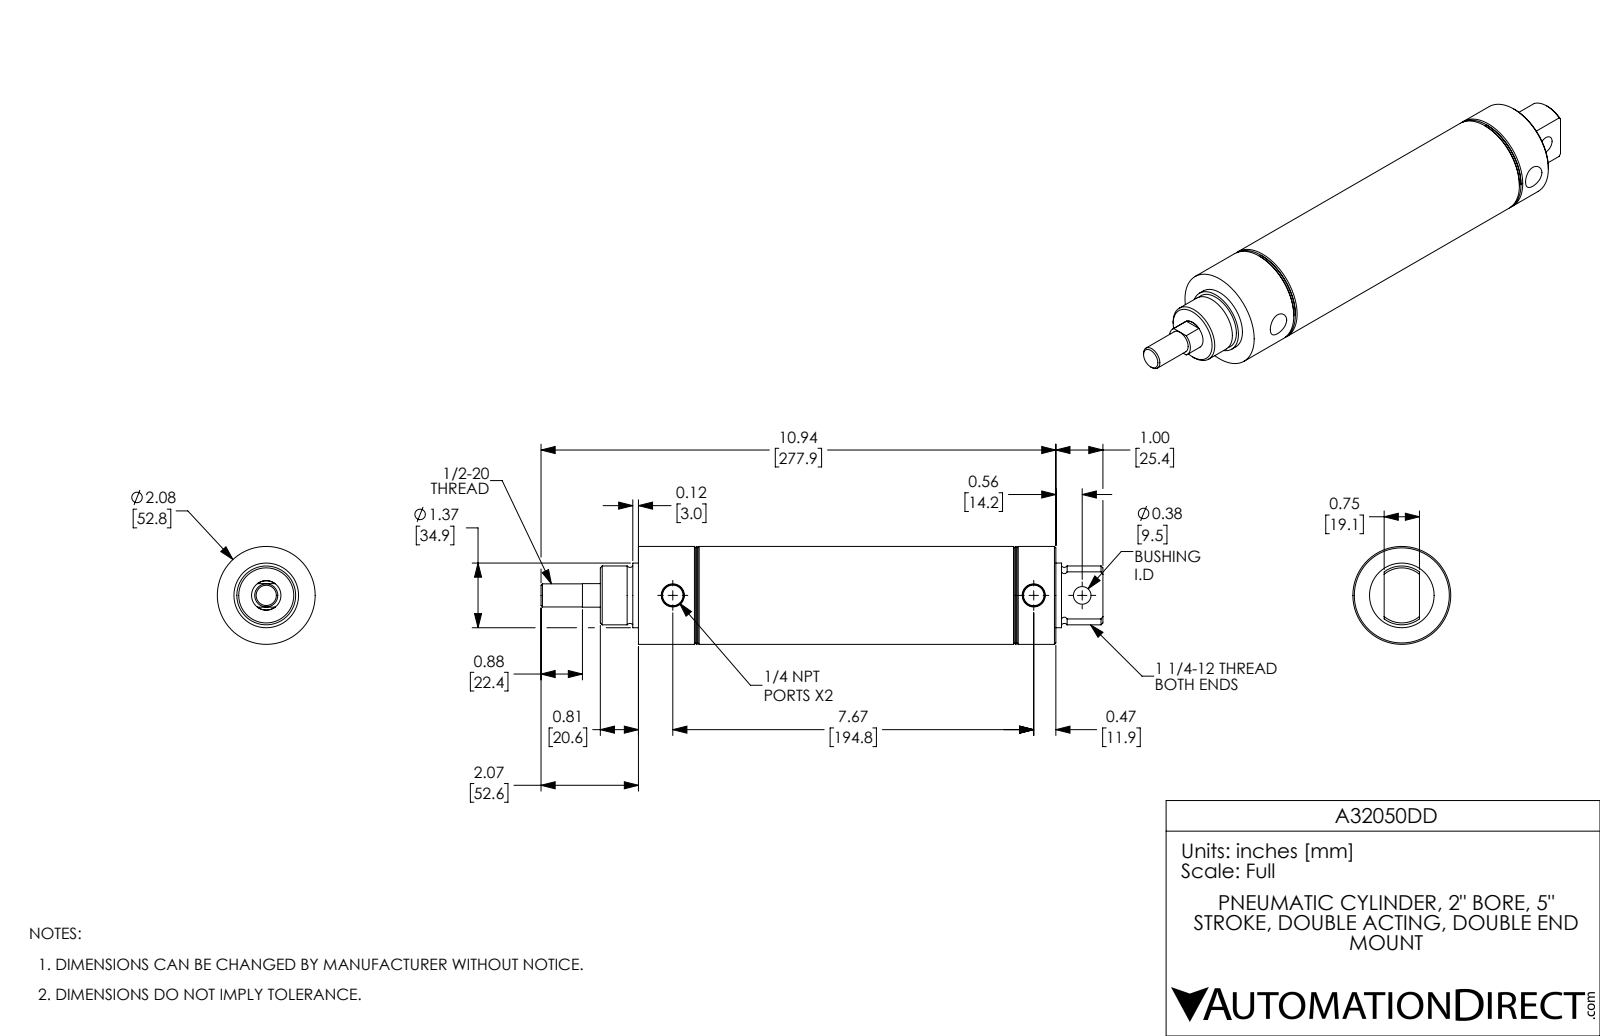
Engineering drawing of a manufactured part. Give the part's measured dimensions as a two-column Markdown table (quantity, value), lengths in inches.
| quantity | value |
| --- | --- |
| part name | A32050DD-MainBody; A32050DD-Rod; A32050DD |
| STEP written by | SolidWorks 2017 (AUTOMOTIVE_DESIGN) |
| units | inches |
| bodies | 2 solids, 88 faces (20 planar, 30 cylindrical, 38 other) |
| overall size | 11.94 × 2.08 × 2.08 |
| volume | 17.8 in³ |
| surface area | 146.2 in² |
| round holes (diameter × count) | 0.438 × 2, 0.375 × 1, 0.625 × 1, 2 × 1 |
| round bosses / shafts (diameter × count) | 2.08 × 1, 1.373 × 1, 1.25 × 1, 0.491 × 1 |
| main face-to-face distances | 1.685, 7.185, 0.5, 5.5, 5, 6.685, 2.185, 8.87, 0.12, 1.805 |
| hole center spacings | 1.03, 7.67, 8.7 |
